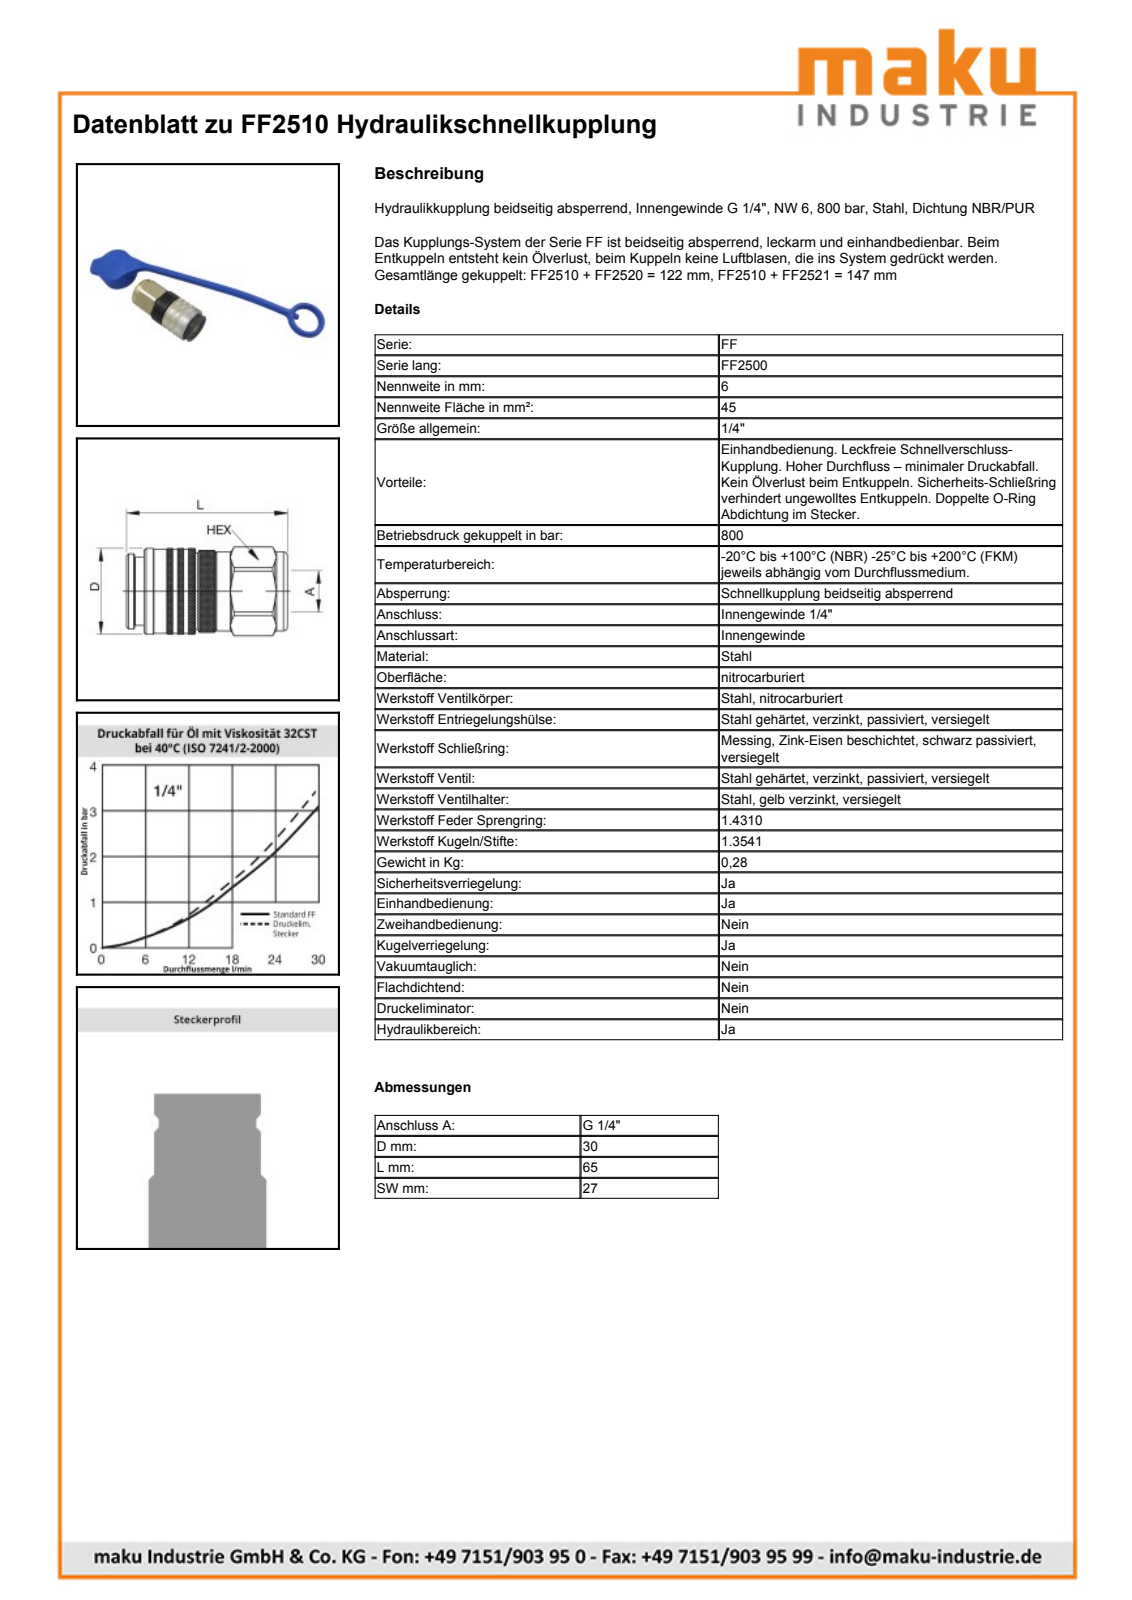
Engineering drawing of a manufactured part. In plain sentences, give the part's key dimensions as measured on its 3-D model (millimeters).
The part is named "FF2510". Its 3-D file was written by "SolidWorks 2009 (AUTOMOTIVE_DESIGN)". It is 1 solid with 134 faces: 26 planar, 50 cylindrical and 58 other. Overall it measures 65.1 by 30 by 30 millimeters. Its volume is 40 483 cubic millimeters and its surface area 8 762 square millimeters. Round holes: 1 of diameter 9.5, 1 of diameter 10.95, 1 of diameter 11.44, 1 of diameter 19.2, 1 of diameter 25.1, 1 of diameter 27.2, 1 of diameter 28. Round bosses or shafts: 1 of diameter 30, 1 of diameter 29.5, 1 of diameter 27.5, 1 of diameter 26.8, 1 of diameter 26.2, 1 of diameter 24.7, 1 of diameter 19.1, 1 of diameter 9.4. The main face-to-face distances are 27, 65.1, 64.13, 0.97, 60.1, 4.03, 5, 11.51, 48.59, 52.62.
